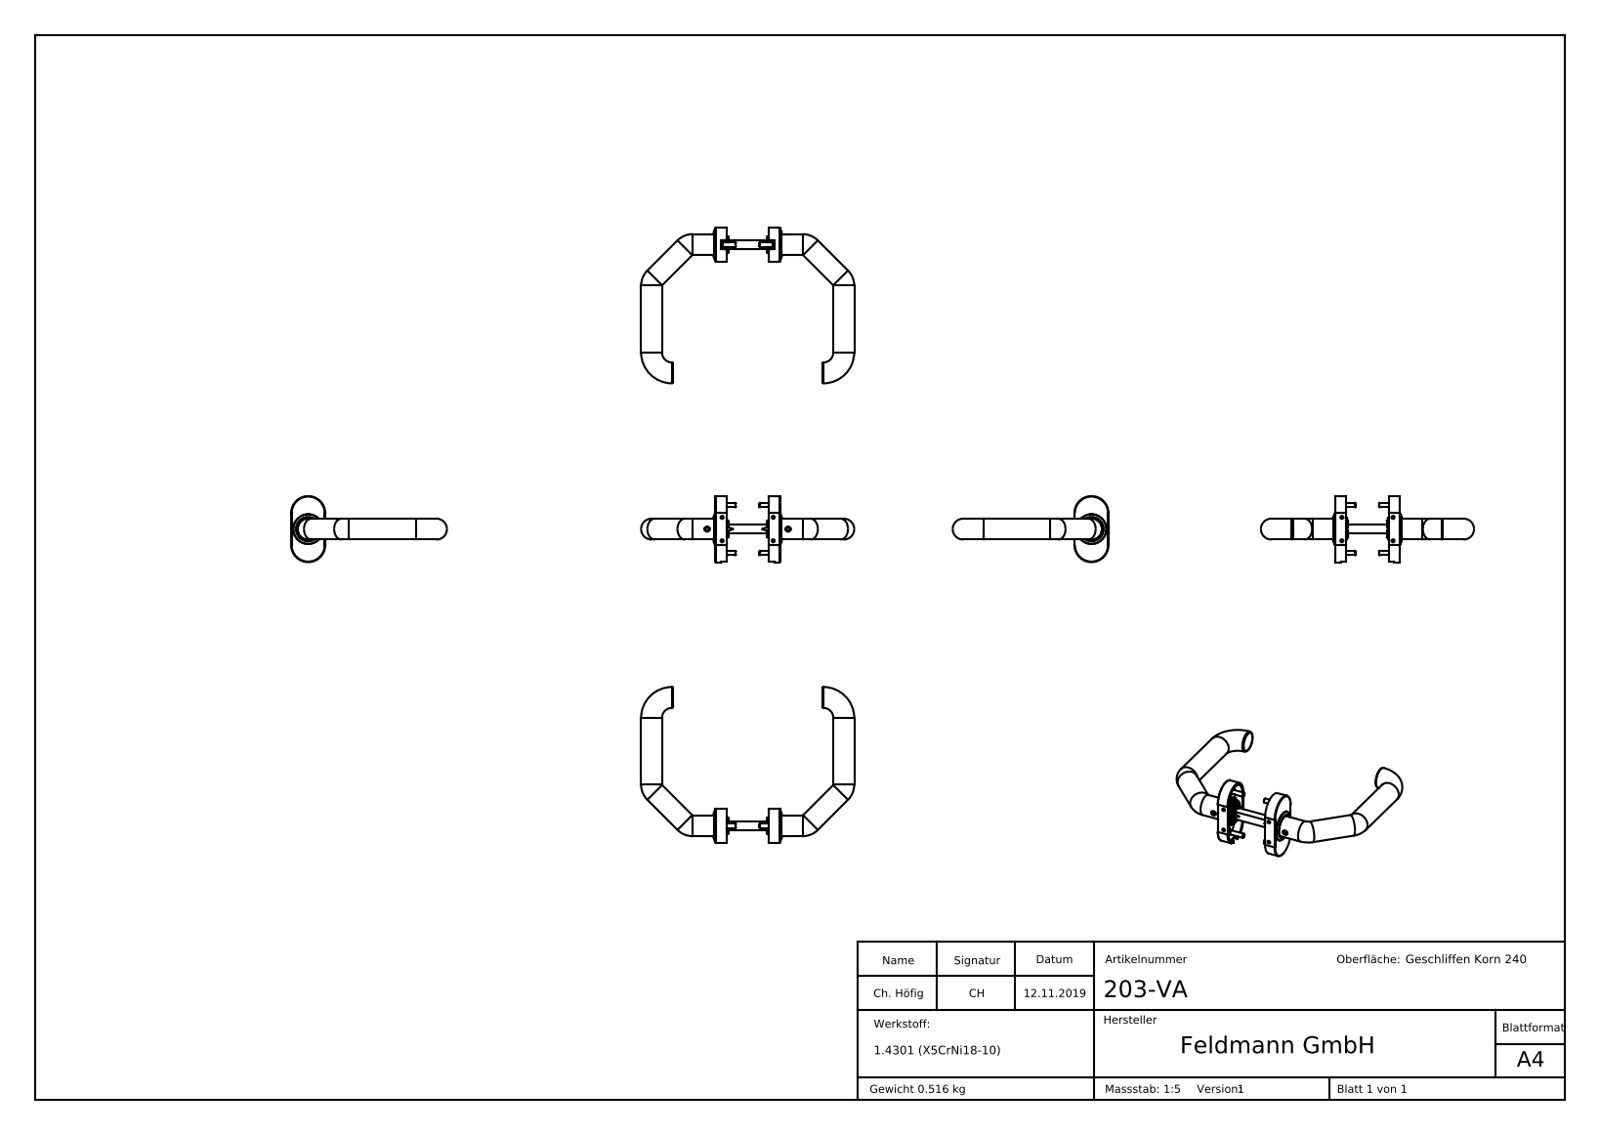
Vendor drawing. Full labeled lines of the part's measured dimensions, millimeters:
Part name (STEP PRODUCT): 203-VA Teil9_203-VA Teil9; 203-VA Teil2_203-VA Teil2; DIN914_DIN 914 M6x6; DIN 965_DIN 965 M4x18 (+8 more)
STEP written by: SolidWorks 2018 (CONFIG_CONTROL_DESIGN)
Units: millimetres
Bodies: 27 solids, 896 faces (462 planar, 158 cylindrical, 276 other)
Overall size (bounding box): 200 × 146.2 × 62
Volume: 64 927 mm³ · Surface area: 80 446 mm²
Round holes (diameter × count): ⌀15.7 ×4, ⌀1.7 ×2, ⌀5 ×2, ⌀6.2 ×2, ⌀13.8 ×1, ⌀16 ×1, ⌀16.3 ×1, ⌀16.9 ×1, ⌀19.05 ×1, ⌀20.6 ×1, ⌀28 ×1
Round bosses / shafts (diameter × count): ⌀19.6 ×5, ⌀7.71 ×2, ⌀7.2 ×2, ⌀6 ×2, ⌀4 ×2, ⌀3.6 ×2, ⌀27.8 ×1, ⌀24 ×1
Partial cylindrical surfaces — rounded edges, fillets, slot ends (radius × count): R0.5 ×16, R0.78 ×4, R8 ×3, R0.75 ×2, R2.5 ×2, R6.9 ×2, R14 ×2, R15 ×2
Main face-to-face distances: 1, 0.9, 2.5, 57, 1.5, 58.5, 59.5, 58, 60.1, 0.6
Hole centre spacings: 8.88, 13.79, 22.5, 31.31, 52.2, 128.2, 2.7, 45
